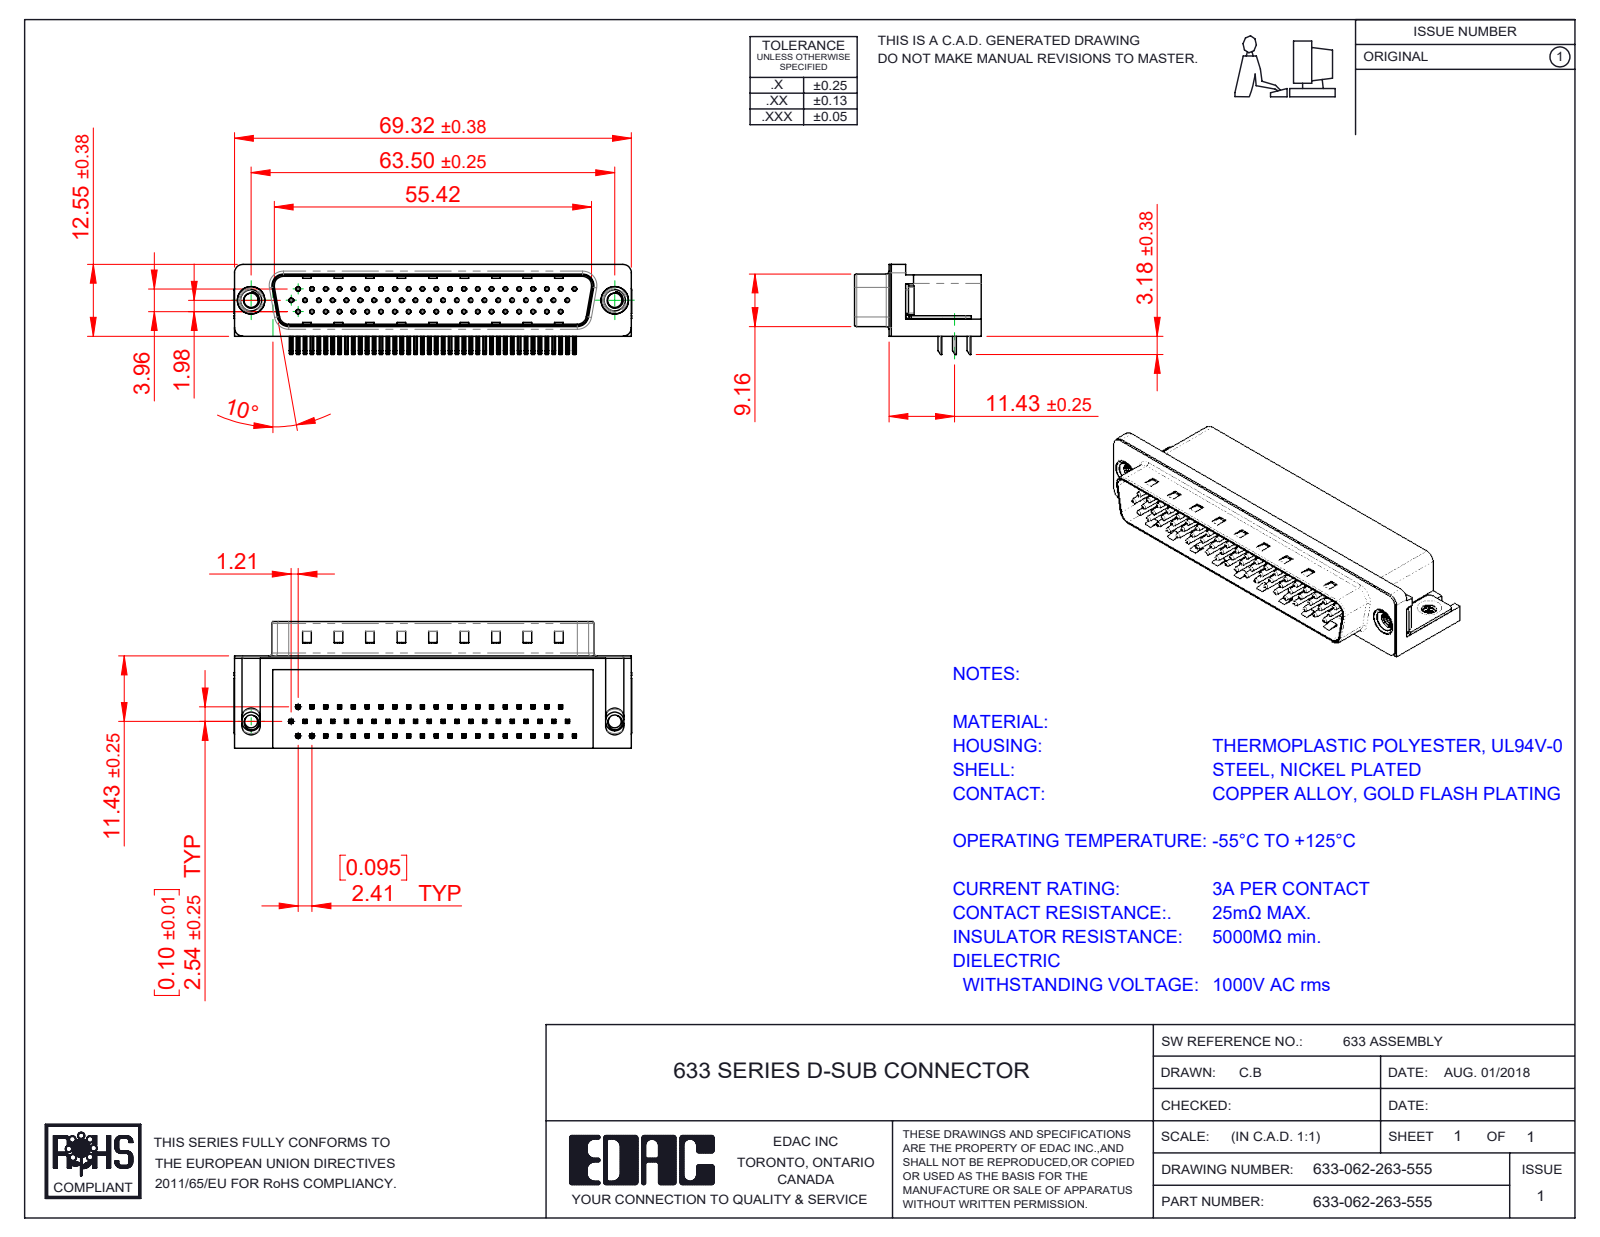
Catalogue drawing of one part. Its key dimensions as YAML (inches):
part_name: "633-062-263-555; 633 Shell_62 Contact; 633 Contact Bottom; 633 Contact Middle (+4 more)"
step_written_by: "SolidWorks 2016 (CONFIG_CONTROL_DESIGN)"
units: inches
bodies: {solids: 68, faces: 5106, planar: 3213, cylindrical: 1458, other: 435}
overall_size: [2.732, 0.87, 0.619]
volume: 0.675
surface_area: 20.91
round_holes:
  - {diameter: 0.014, count: 62}
  - {diameter: 0.031, count: 62}
  - {diameter: 0.089, count: 2}
  - {diameter: 0.098, count: 2}
  - {diameter: 0.157, count: 2}
  - {diameter: 0.189, count: 2}
  - {diameter: 0.197, count: 2}
round_bosses_or_shafts:
  - {diameter: 0.03, count: 62}
  - {diameter: 0.193, count: 2}
  - {diameter: 0.187, count: 2}
  - {diameter: 0.154, count: 2}
  - {diameter: 0.128, count: 2}
partial_cylinders:
  - {radius: 0.01, count: 256}
  - {radius: 0.005, count: 124}
  - {radius: 0.039, count: 16}
  - {radius: 0.02, count: 9}
  - {radius: 0.063, count: 8}
  - {radius: 0.059, count: 7}
  - {radius: 0.035, count: 4}
  - {radius: 0.079, count: 4}
face_to_face_distances: [0.016, 0.407, 0.618, 0.345, 0.114, 0.098, 0.1, 0.329, 0.083, 0.634]
hole_center_spacings: [0.095, 0.19, 0.285, 0.38, 0.57, 0.665, 0.19, 0.285]
